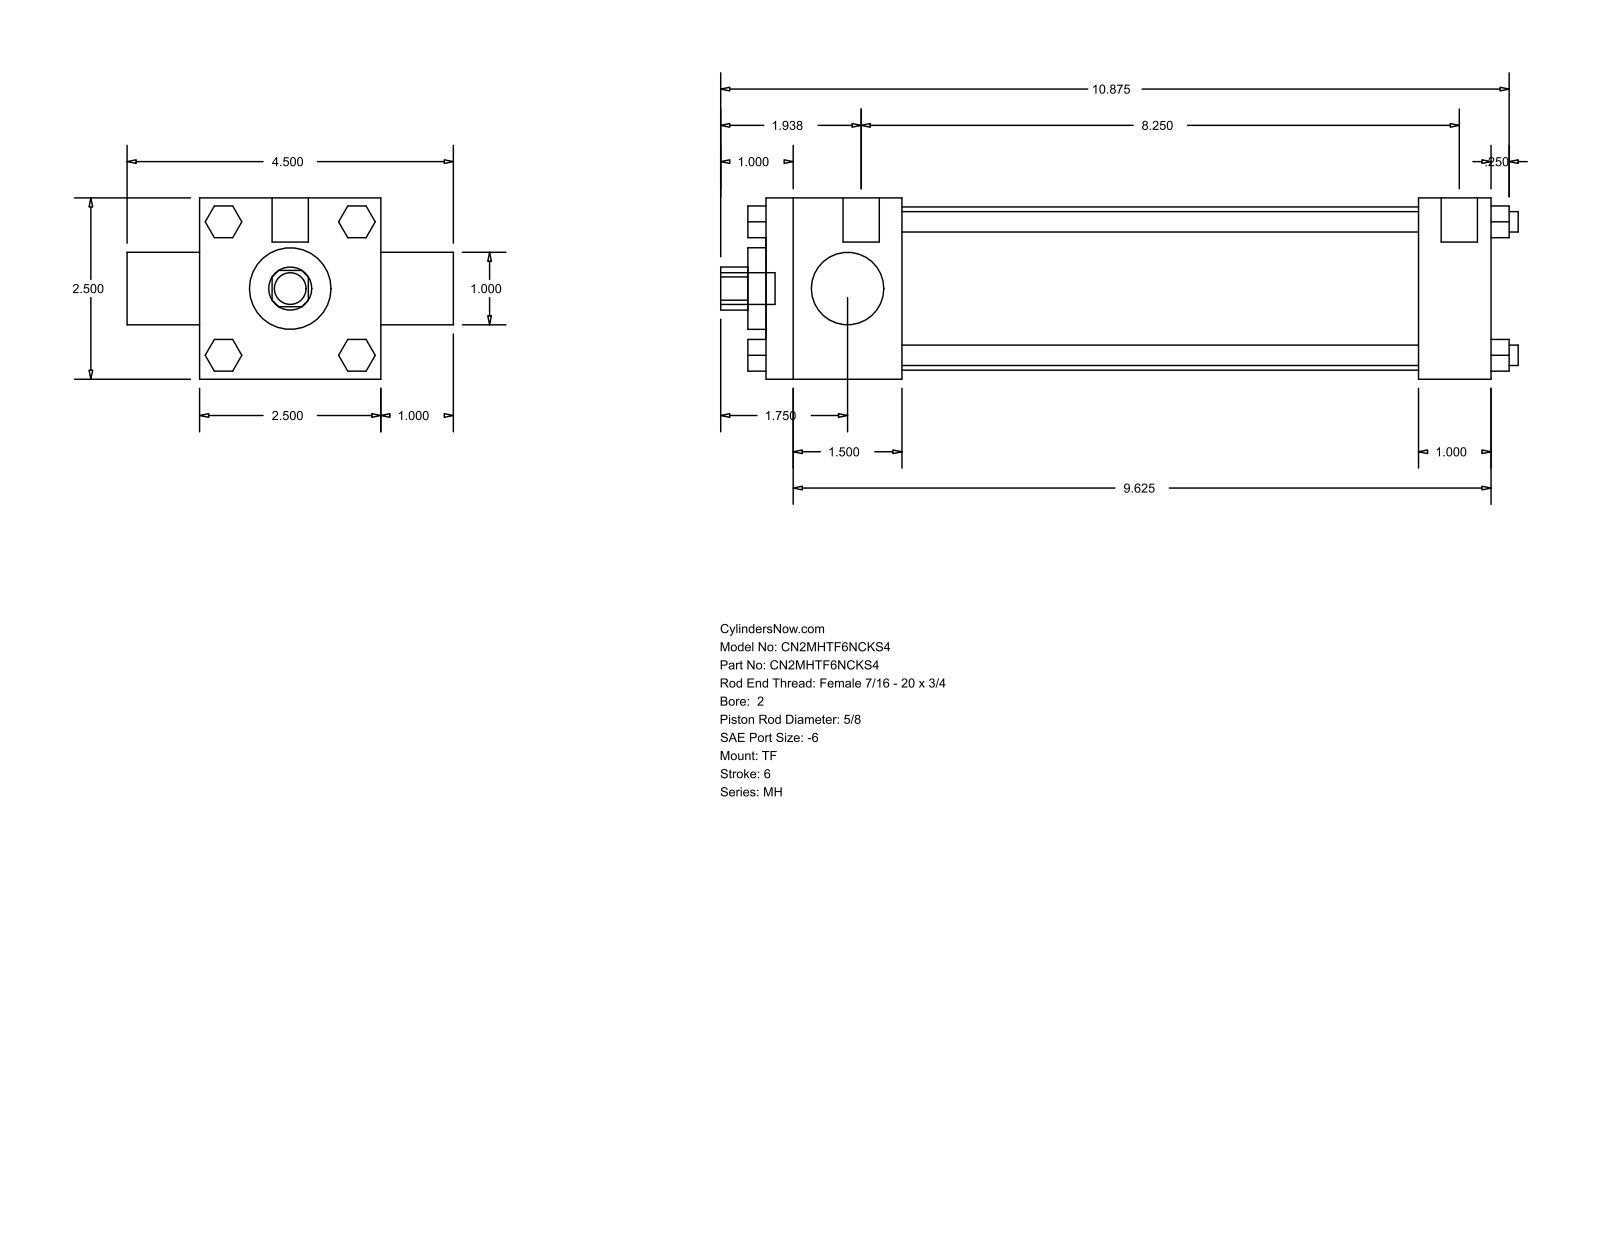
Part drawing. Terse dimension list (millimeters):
name: MH_TF__0200_0.625
written by: GSSL Pune (CONFIG_CONTROL_DESIGN)
unit: mm
bodies: 0 solids, 120 faces (92 planar, 28 cylindrical, 0 other)
size: 279.4 × 114.3 × 63.5
holes: 1× ⌀15.88, 1× ⌀25.4, 1× ⌀28.57, 1× ⌀57.15
bosses: 4× ⌀7.14, 3× ⌀5.56, 2× ⌀12.7, 1× ⌀11.11
rounds: 1× R7.54
face distances: 63.5, 254, 47.62, 228.59, 180.97, 206.38, 25.41, 25.4, 260.35, 6.35
